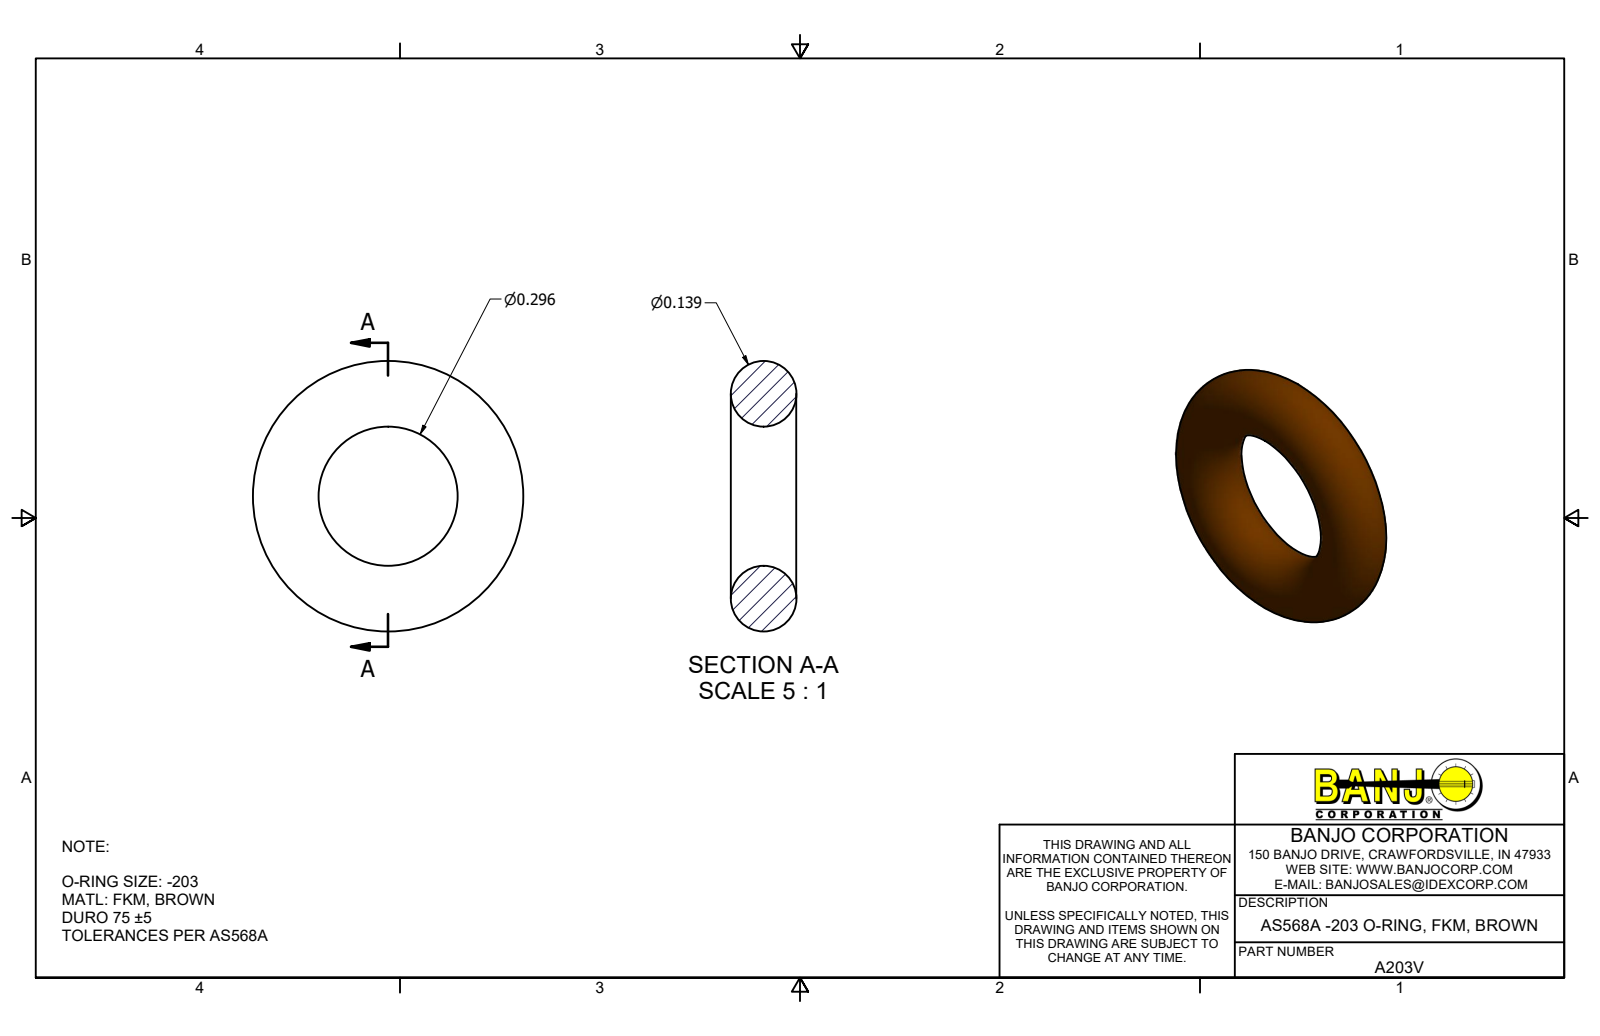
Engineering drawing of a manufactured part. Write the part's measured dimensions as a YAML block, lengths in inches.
part_name: "A203V"
step_written_by: "Autodesk Inventor 2019 (AUTOMOTIVE_DESIGN)"
units: inches
bodies: {solids: 1, faces: 1, planar: 0, cylindrical: 0, other: 1}
overall_size: [0.574, 0.574, 0.139]
volume: 0.021
surface_area: 0.597
